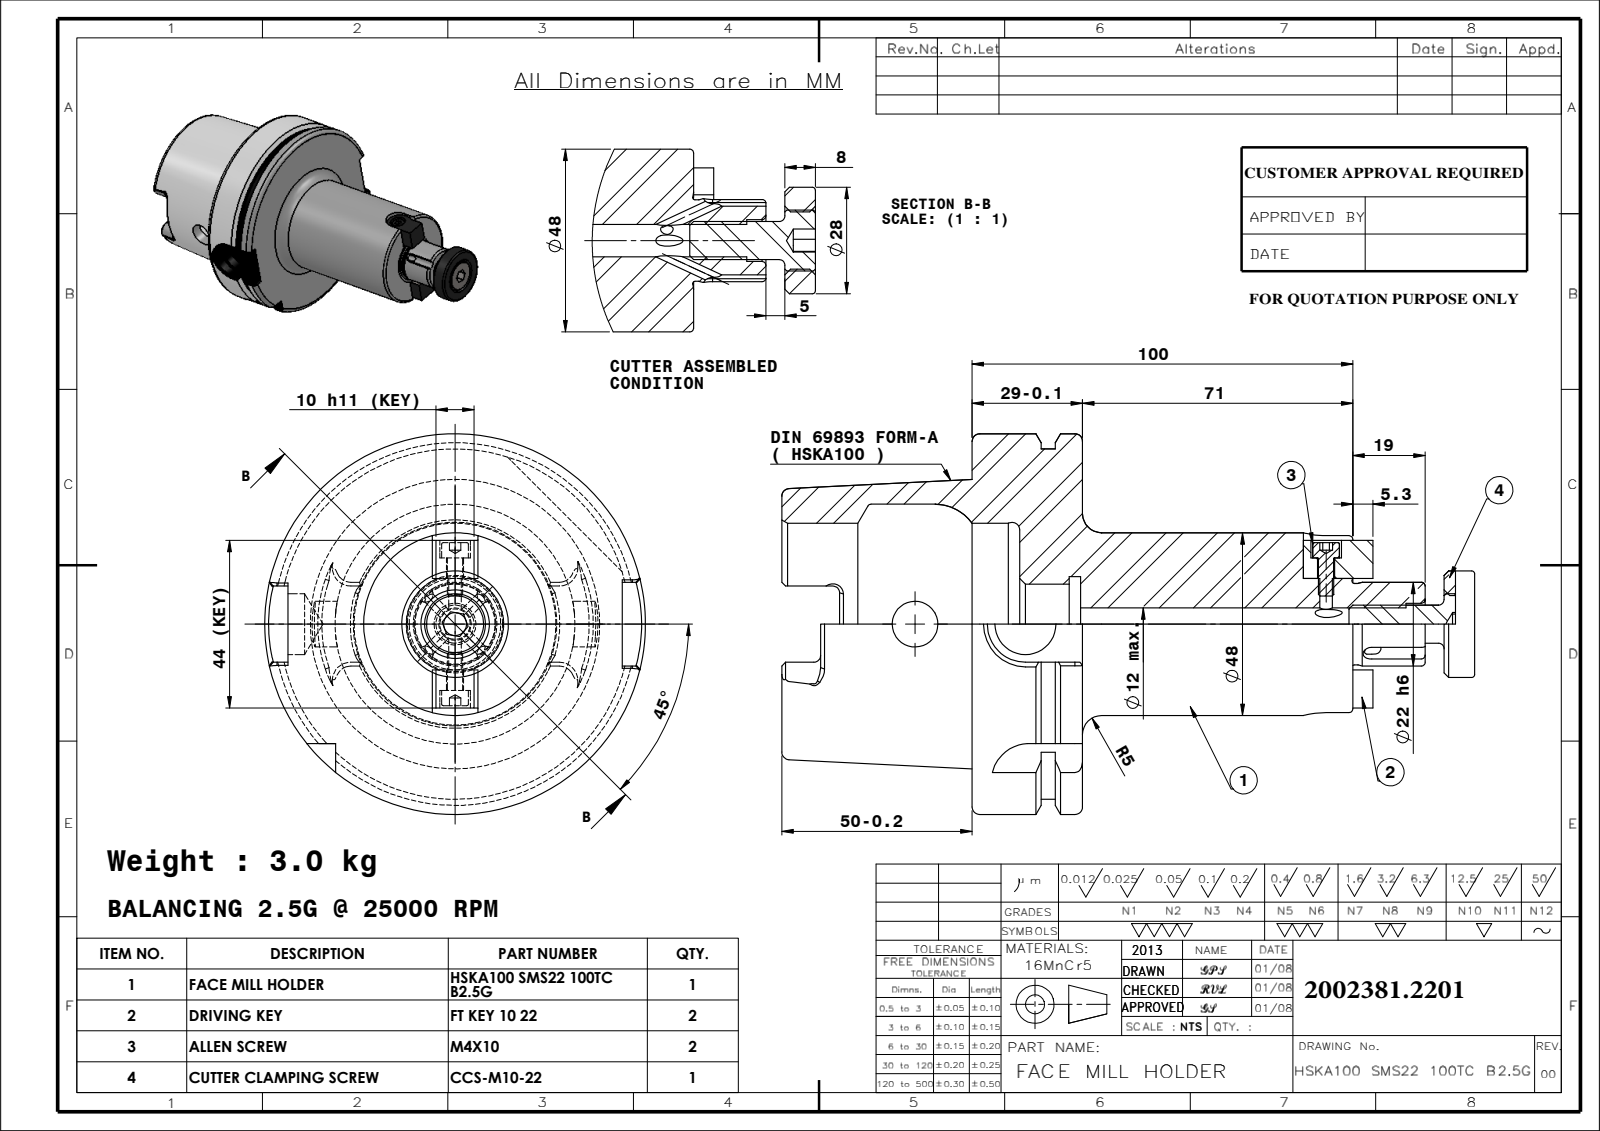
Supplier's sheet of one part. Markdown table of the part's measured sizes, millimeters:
| quantity | value |
| --- | --- |
| part name | HSKA100 SMS22 100TC B2.5G; FT KEY 10 22; M4X10_DIN 912 M4 x 10 --- 10N; CCS-M10-22 (+2 more) |
| STEP written by | SolidWorks 2009 (CONFIG_CONTROL_DESIGN) |
| units | millimeters |
| bodies | 7 solids, 360 faces (136 planar, 98 cylindrical, 126 other) |
| overall size | 182 × 100 × 100 |
| volume | 390 302 mm³ |
| surface area | 70 944 mm² |
| round holes (diameter × count) | 3 × 4, 3.3 × 1, 4.5 × 1, 8 × 1, 8.5 × 1, 11 × 1, 12 × 1, 15 × 1, 16 × 1, 21 × 1, 25 × 1, 53 × 1 |
| round bosses / shafts (diameter × count) | 100 × 1, 92 × 1, 48 × 1, 28 × 1, 22 × 1, 21.4 × 1, 16 × 1, 10 × 1 |
| partial cylindrical surfaces (radius × count) | 1.8 × 6, 2 × 4, 4.88 × 4, 10 × 2, 6 × 1, 11 × 1 |
| main face-to-face distances | 29, 12.5, 16.5, 100, 87.5, 71, 50, 62.5, 79, 150 |
| hole center spacings | 29 |
